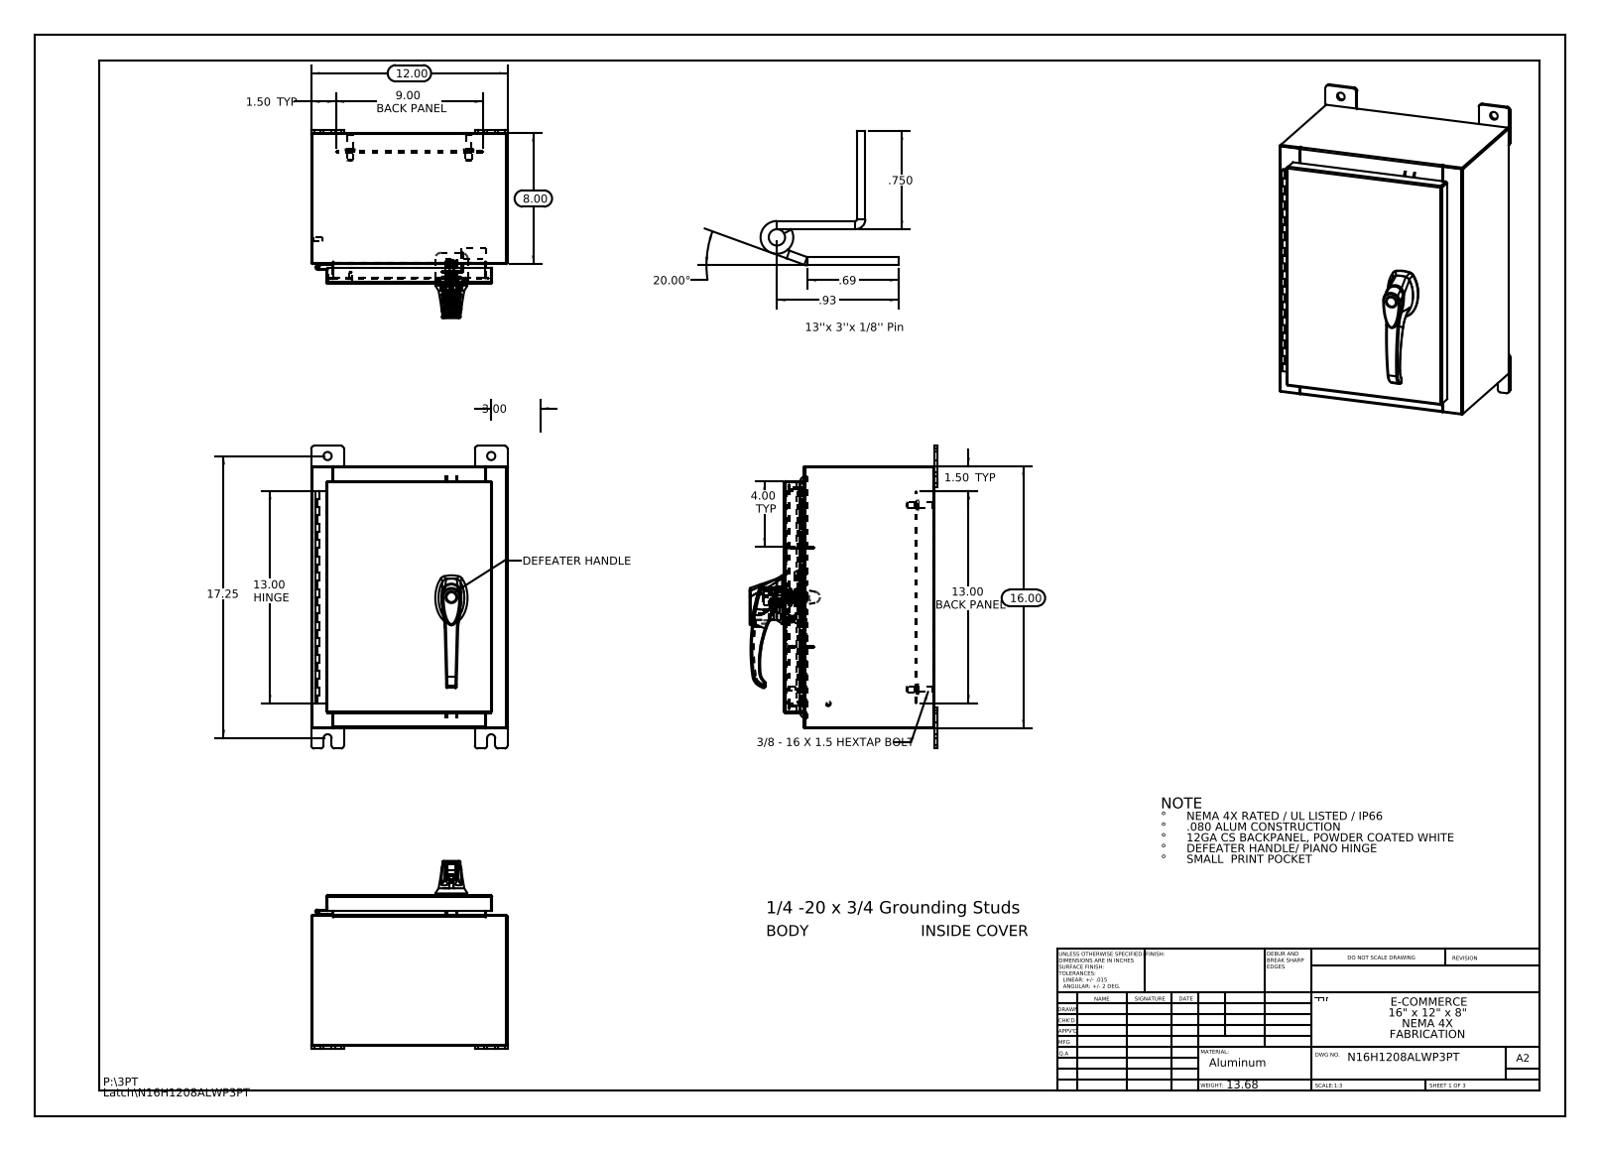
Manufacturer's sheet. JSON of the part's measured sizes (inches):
{"part_name": "00005310_26163101; 022151; N16H1208ALWP3PT Top; N16H1208ALWP3PT Mounting Feet (+8 more)", "step_written_by": "SolidWorks 2013 (CONFIG_CONTROL_DESIGN)", "units": "inches", "bodies": {"solids": 37, "faces": 2290, "planar": 775, "cylindrical": 817, "other": 698}, "overall_size": [18.5, 12, 11.495], "volume_in3": 97.24, "surface_area_in2": 2393, "round_holes": [[0.5, 8], [0.25, 4], [0.138, 3], [0.161, 3], [0.079, 2], [0.203, 2], [0.313, 2], [0.437, 2], [0.125, 1], [0.125, 1], [0.197, 1], [0.276, 1]], "round_bosses_or_shafts": [[0.625, 4], [0.375, 4], [0.33, 4], [0.157, 4], [0.14, 4], [0.315, 3], [0.236, 3], [1.181, 1]], "partial_cylinders_radius": [[0.118, 37], [0.006, 33], [0.19, 24], [0.013, 20], [0.088, 18], [0.039, 15], [0.028, 12], [0.008, 6]], "face_to_face_distances": [0.075, 9.126, 11.925, 15.925, 9.051, 9.201, 7.925, 1.201, 11.85, 12], "hole_center_spacings": [3.708, 0.295, 0.625, 0.841, 1.25, 1.313, 1.32, 1.484]}
